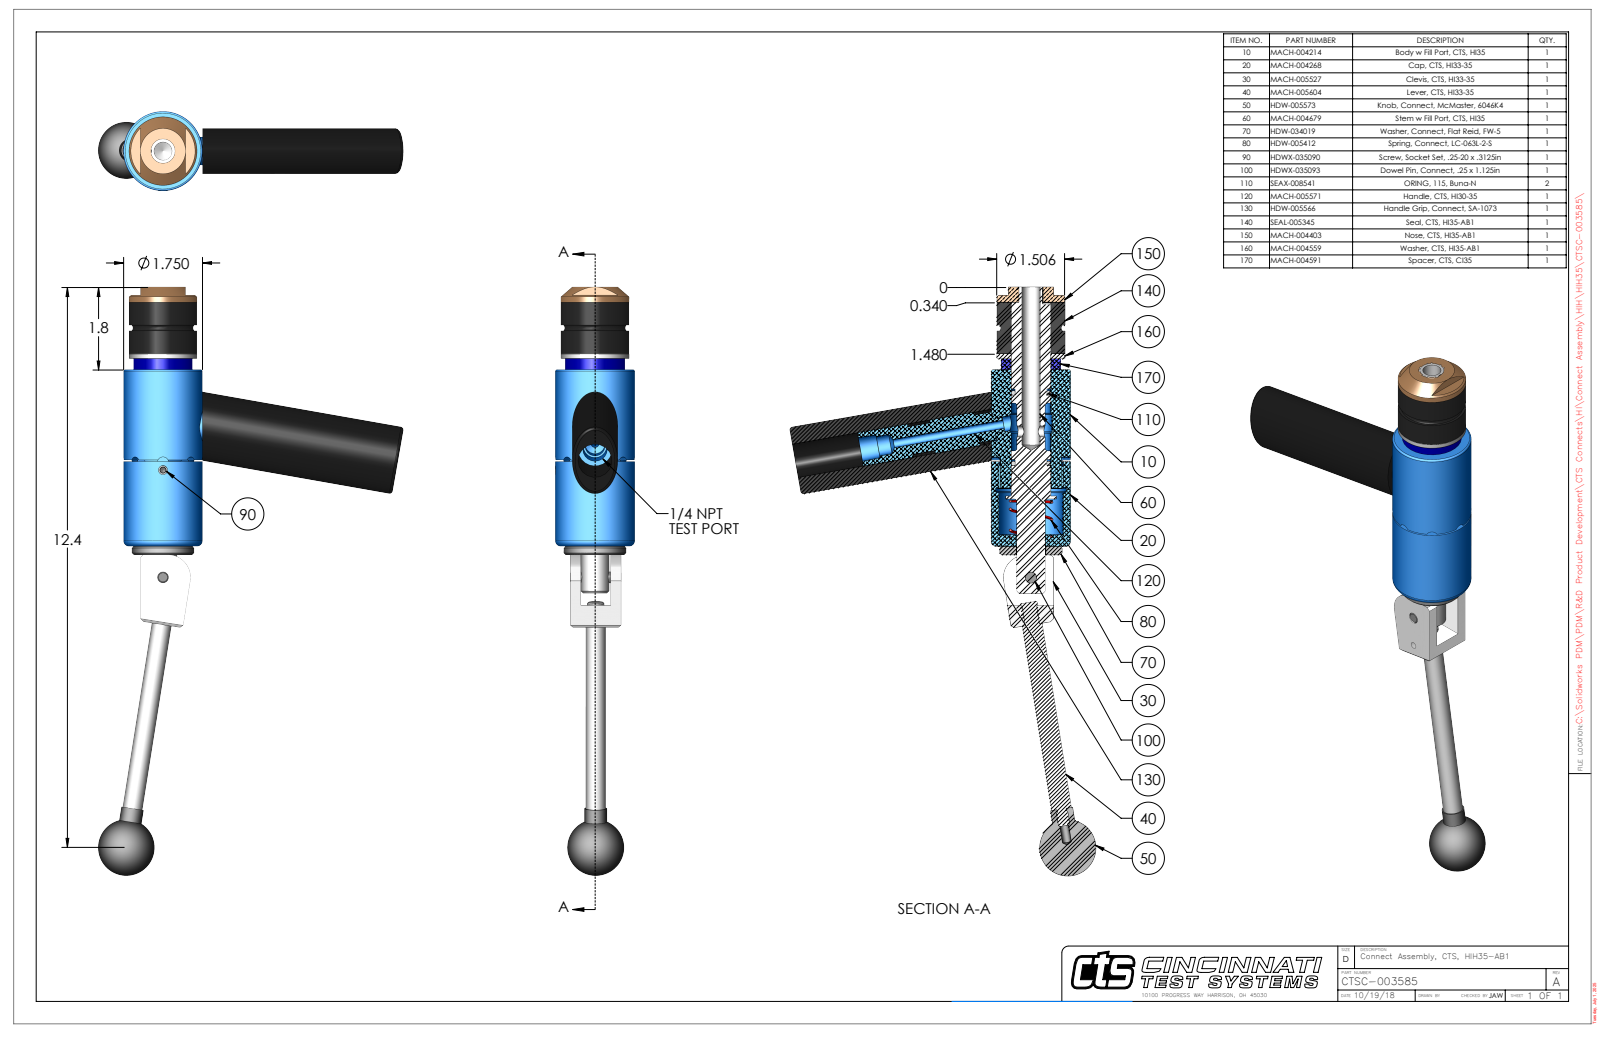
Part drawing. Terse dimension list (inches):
name: CTSC-003585
written by: SolidWorks 2023 (AUTOMOTIVE_DESIGN)
unit: in
bodies: 12 solids, 305 faces (110 planar, 125 cylindrical, 70 other)
size: 13.042 × 6.763 × 1.75
volume: 19.39 in³; area: 129.5 in²
holes: 2× ⌀0.201, 1× ⌀0.15, 1× ⌀0.187, 1× ⌀0.249, 1× ⌀0.25, 1× ⌀0.251, 1× ⌀0.313, 1× ⌀0.406, 1× ⌀0.438, 1× ⌀0.531, 1× ⌀0.635, 1× ⌀0.656
bosses: 2× ⌀0.25, 1× ⌀1.75, 1× ⌀1.506, 1× ⌀1.38, 1× ⌀1.312, 1× ⌀0.869, 1× ⌀0.75, 1× ⌀0.625
rounds: 4× R0.125, 2× R0.029, 1× R0.244, 1× R0.33, 1× R0.5, 1× R0.695, 1× R0.825
face distances: 5.405, 1.49, 3.915, 1.14, 0.35, 4.265, 1.25, 0.11, 0.24, 4.155
hole spacings: 0.74, 2.376, 3.116
